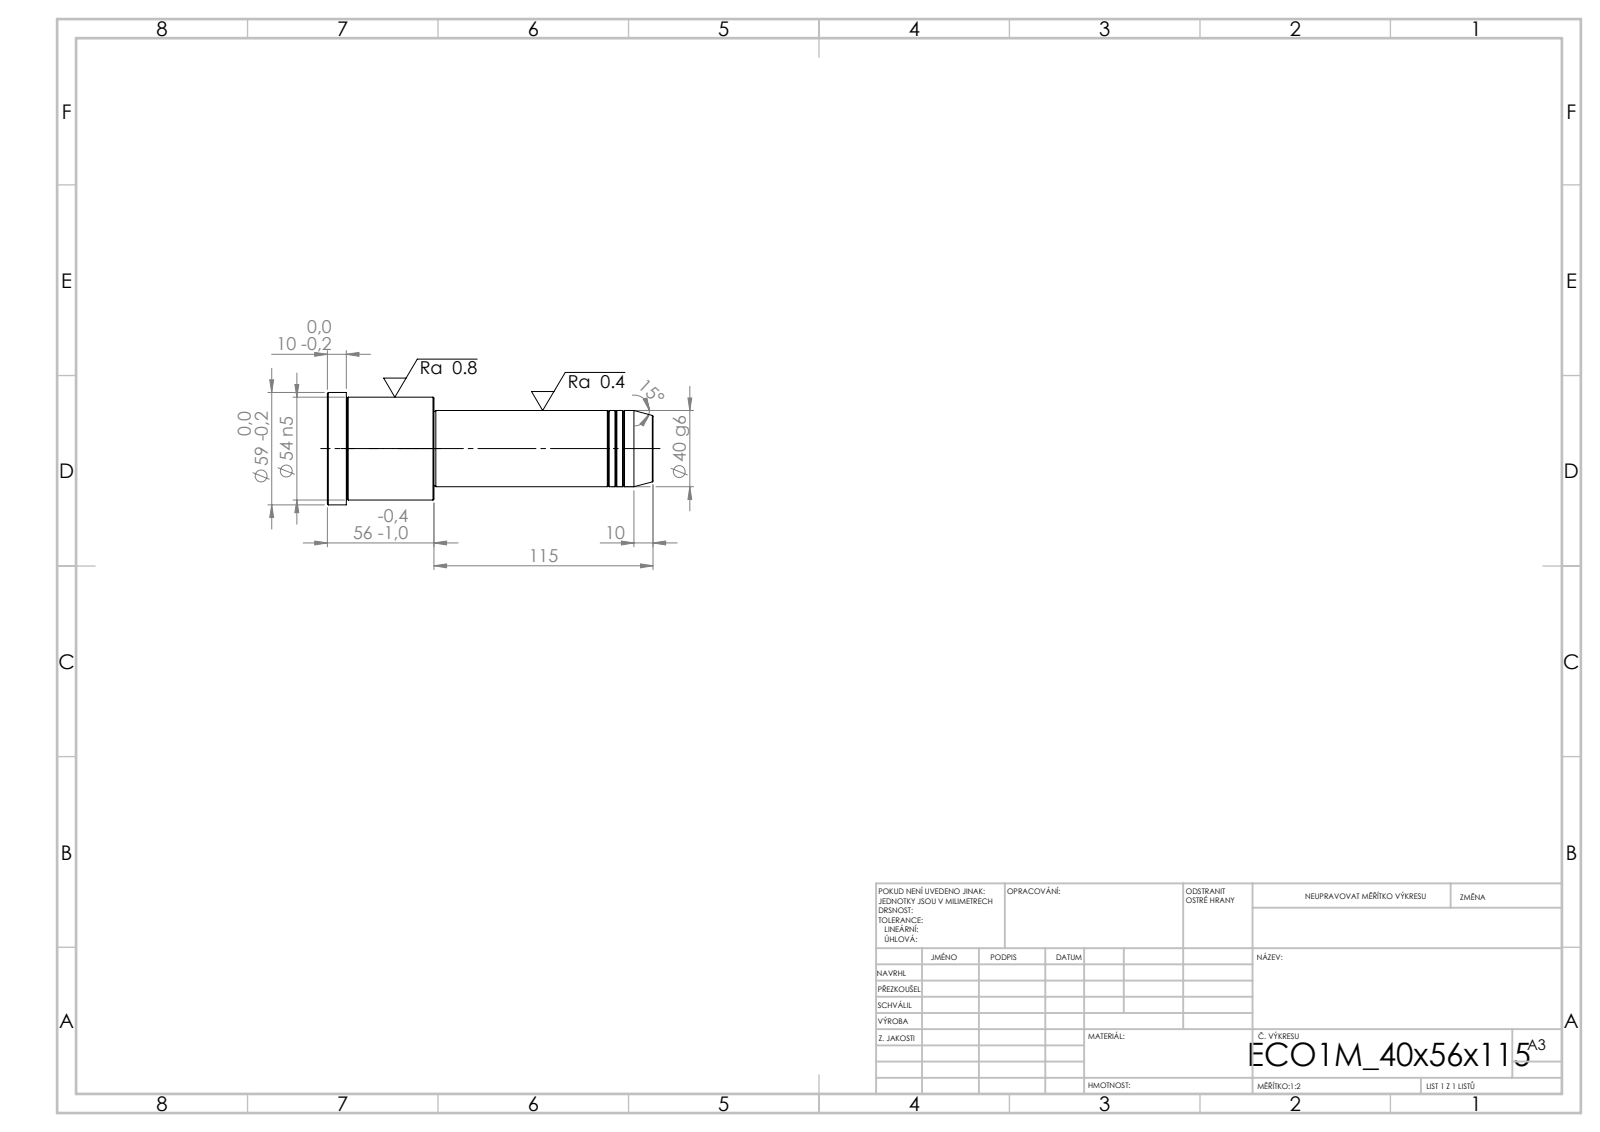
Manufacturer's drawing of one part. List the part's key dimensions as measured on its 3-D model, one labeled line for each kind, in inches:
STEP written by: SolidWorks 2019 (CONFIG_CONTROL_DESIGN)
Units: inches
Bodies: 1 solid, 43 faces (5 planar, 14 cylindrical, 24 other)
Overall size (bounding box): 6.732 × 2.323 × 2.323
Volume: 16.8 in³ · Surface area: 45.76 in²
Round bosses / shafts (diameter × count): ⌀2.323 ×1, ⌀2.126 ×1, ⌀1.575 ×1, ⌀1.535 ×1
Main face-to-face distances: 2.205, 4.528, 6.732, 6.339, 1.811, 0.394, 4.488, 0.039, 1.85, 2.244
